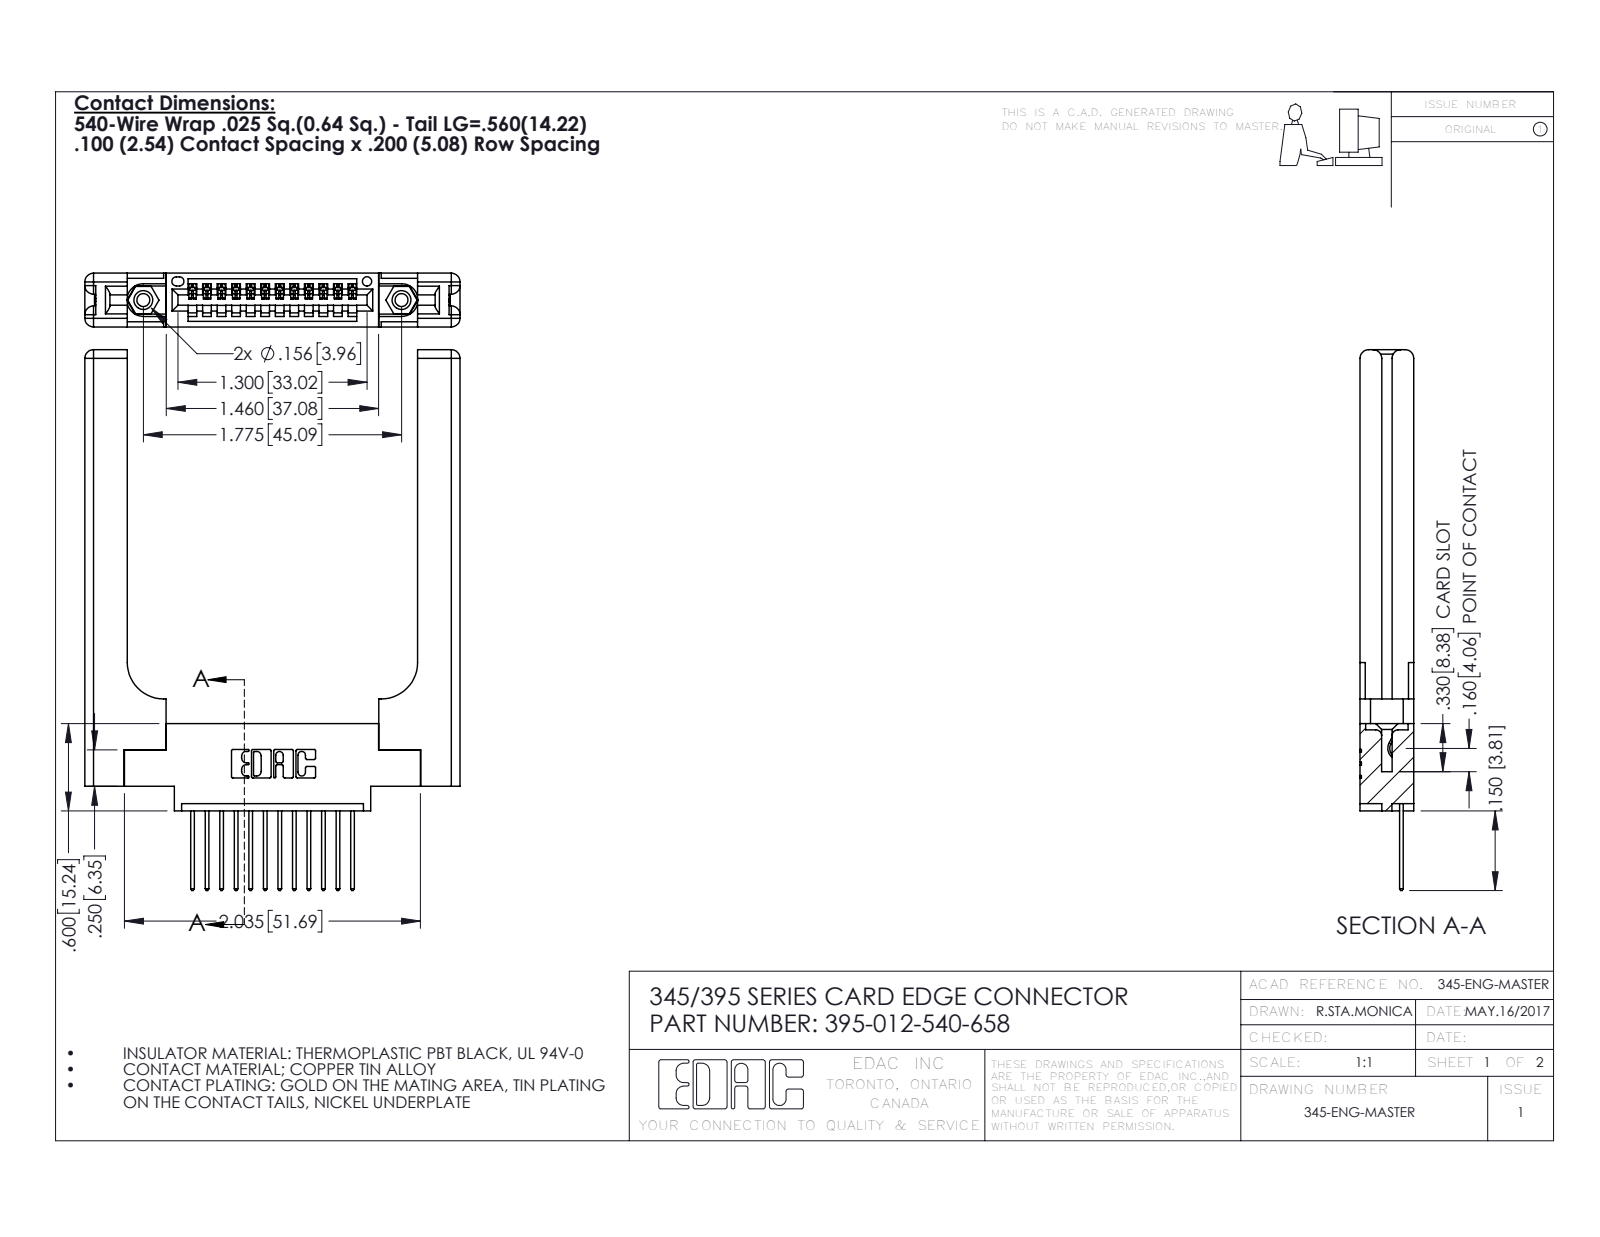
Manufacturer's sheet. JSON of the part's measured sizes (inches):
{"part_name": "345-220-058_345-220-058; 345 Part_0.170 Offset - 0.156 Dia-TH; 345-292-001_345-293-140; 345-250-001_345-250-001-102 (+1 more)", "step_written_by": "SolidWorks 2016 (CONFIG_CONTROL_DESIGN)", "units": "inches", "bodies": {"solids": 17, "faces": 1082, "planar": 712, "cylindrical": 310, "other": 60}, "overall_size": [3.717, 2.579, 0.37], "volume_in3": 0.878, "surface_area_in2": 20.08, "round_holes": [[0.089, 2], [0.125, 2], [0.156, 2], [0.064, 1]], "round_bosses_or_shafts": [[0.155, 2]], "partial_cylinders_radius": [[0.006, 24], [0.01, 24], [0.01, 22], [0.06, 16], [0.007, 6], [0.031, 6], [0.026, 3], [0.03, 2]], "face_to_face_distances": [0.37, 0.072, 0.15, 0.298, 0.22, 0.148, 0.077, 1.996, 0.123, 0.098], "hole_center_spacings": [0.27, 1.543, 1.775]}
